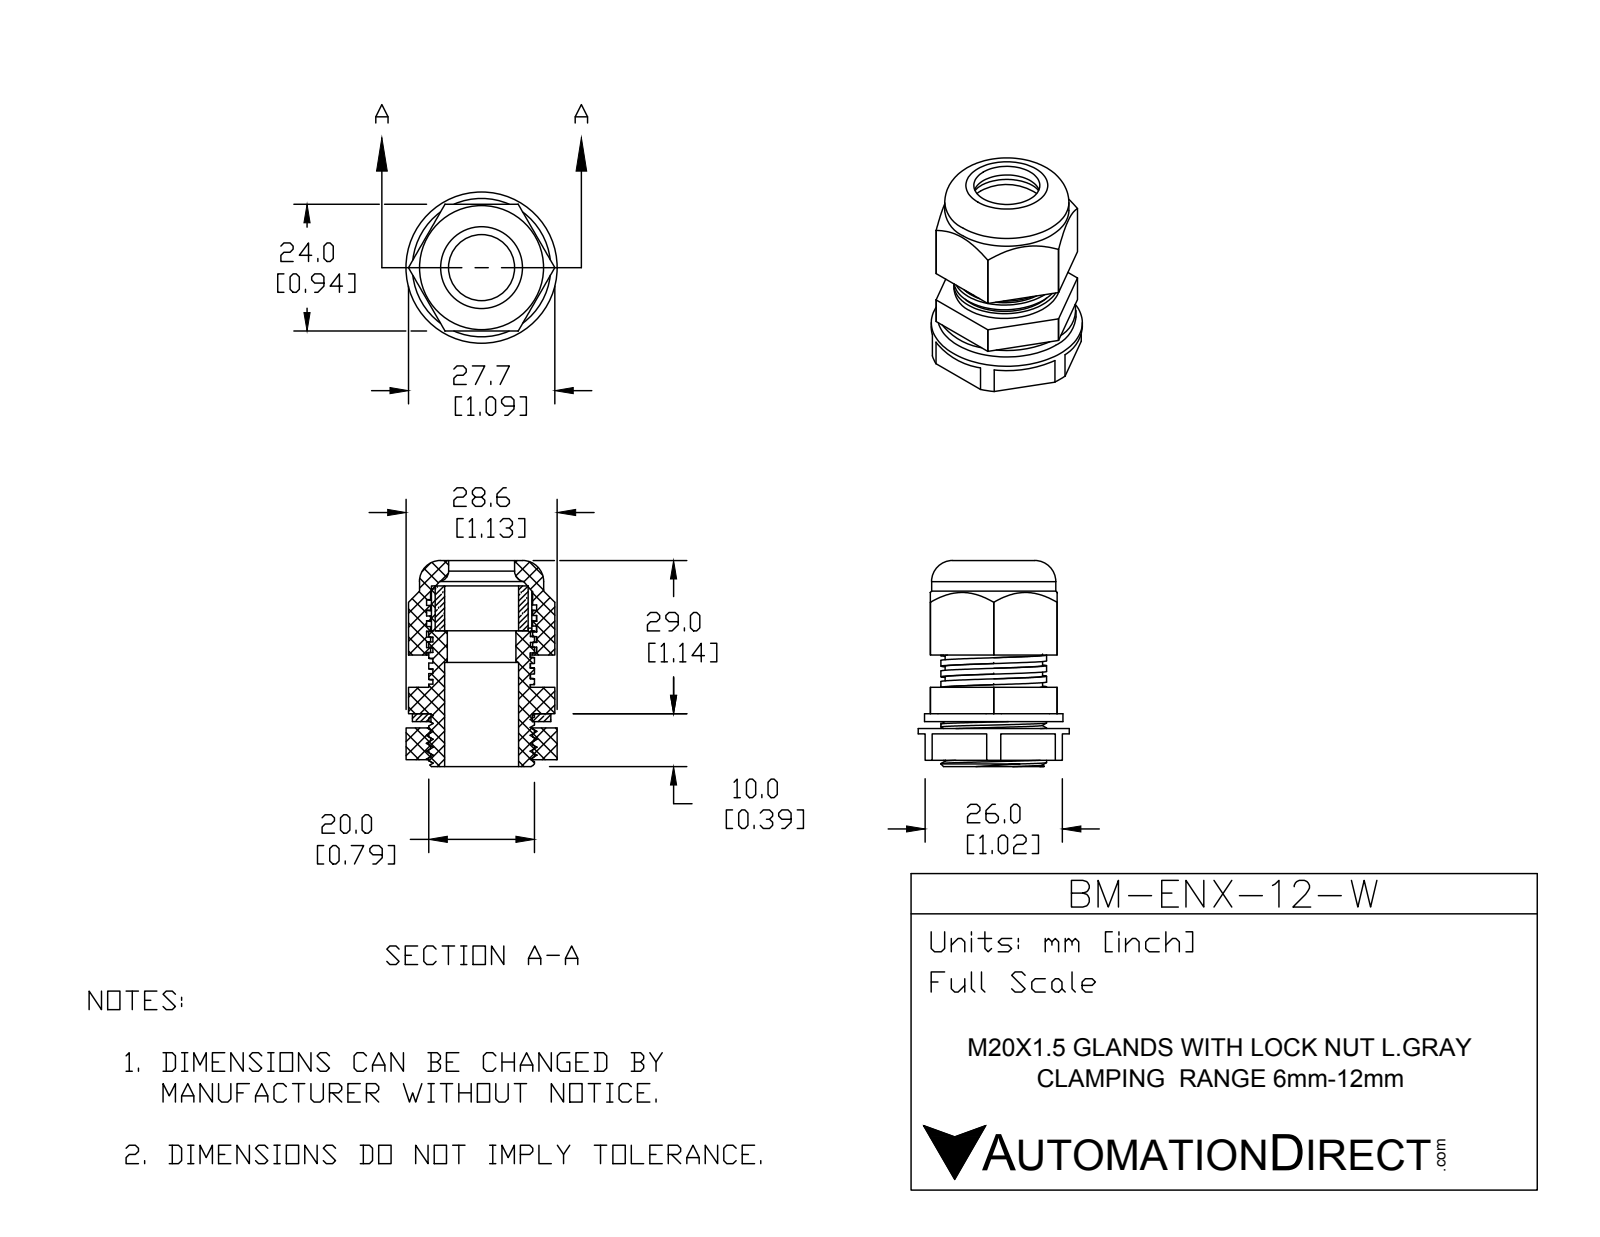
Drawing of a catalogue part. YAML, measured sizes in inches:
part_name: "BM-ENX-12-W"
step_written_by: "SolidWorks 2015 (CONFIG_CONTROL_DESIGN)"
units: inches
bodies: {solids: 5, faces: 247, planar: 141, cylindrical: 84, other: 22}
overall_size: [1.535, 1.126, 1.126]
volume: 0.694
surface_area: 19.22
round_holes:
  - {diameter: 0.492, count: 1}
  - {diameter: 0.512, count: 1}
  - {diameter: 0.551, count: 1}
  - {diameter: 0.693, count: 1}
  - {diameter: 0.756, count: 1}
  - {diameter: 0.761, count: 1}
round_bosses_or_shafts:
  - {diameter: 1.126, count: 1}
  - {diameter: 1.031, count: 1}
  - {diameter: 0.925, count: 1}
  - {diameter: 0.787, count: 1}
  - {diameter: 0.748, count: 1}
partial_cylinders:
  - {radius: 0.545, count: 1}
face_to_face_distances: [0.945, 0.039, 0.984, 0.342, 0.106, 0.236, 0.197, 0.283, 0.047, 0.059]
